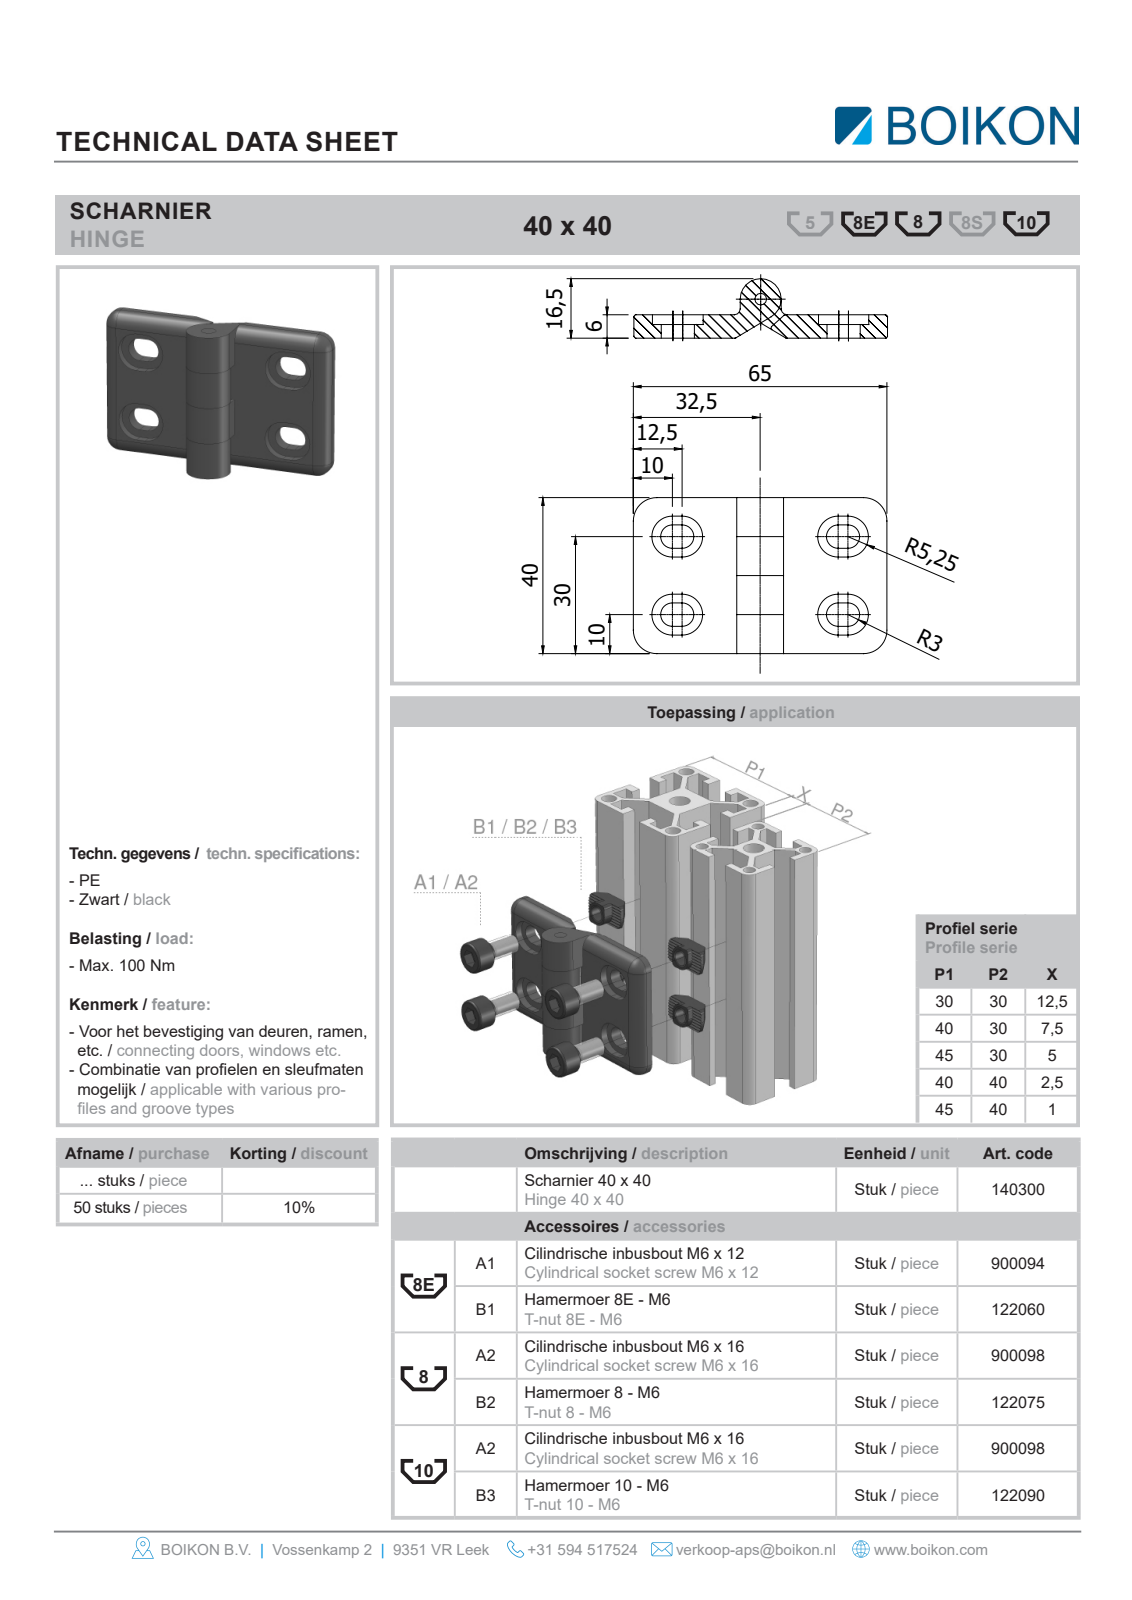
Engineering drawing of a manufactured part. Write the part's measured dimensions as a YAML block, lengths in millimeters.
part_name: "Root; 140300Scharnier 40x40, 8 en 10BOIKON"
step_written_by: "HiCAD 2013 1802.4 Build 509 (AUTOMOTIVE_DESIGN)"
units: millimeters
bodies: {solids: 3, faces: 87, planar: 48, cylindrical: 35, other: 4}
overall_size: [65, 40, 16]
volume: 16207
surface_area: 9258
round_holes:
  - {diameter: 4, count: 1}
round_bosses_or_shafts:
  - {diameter: 12, count: 1}
partial_cylinders:
  - {radius: 3.1, count: 8}
  - {radius: 4, count: 8}
  - {radius: 5.2, count: 8}
face_to_face_distances: [6, 10, 20, 30, 3.7, 2.3, 40, 26.5, 38.5, 12]
